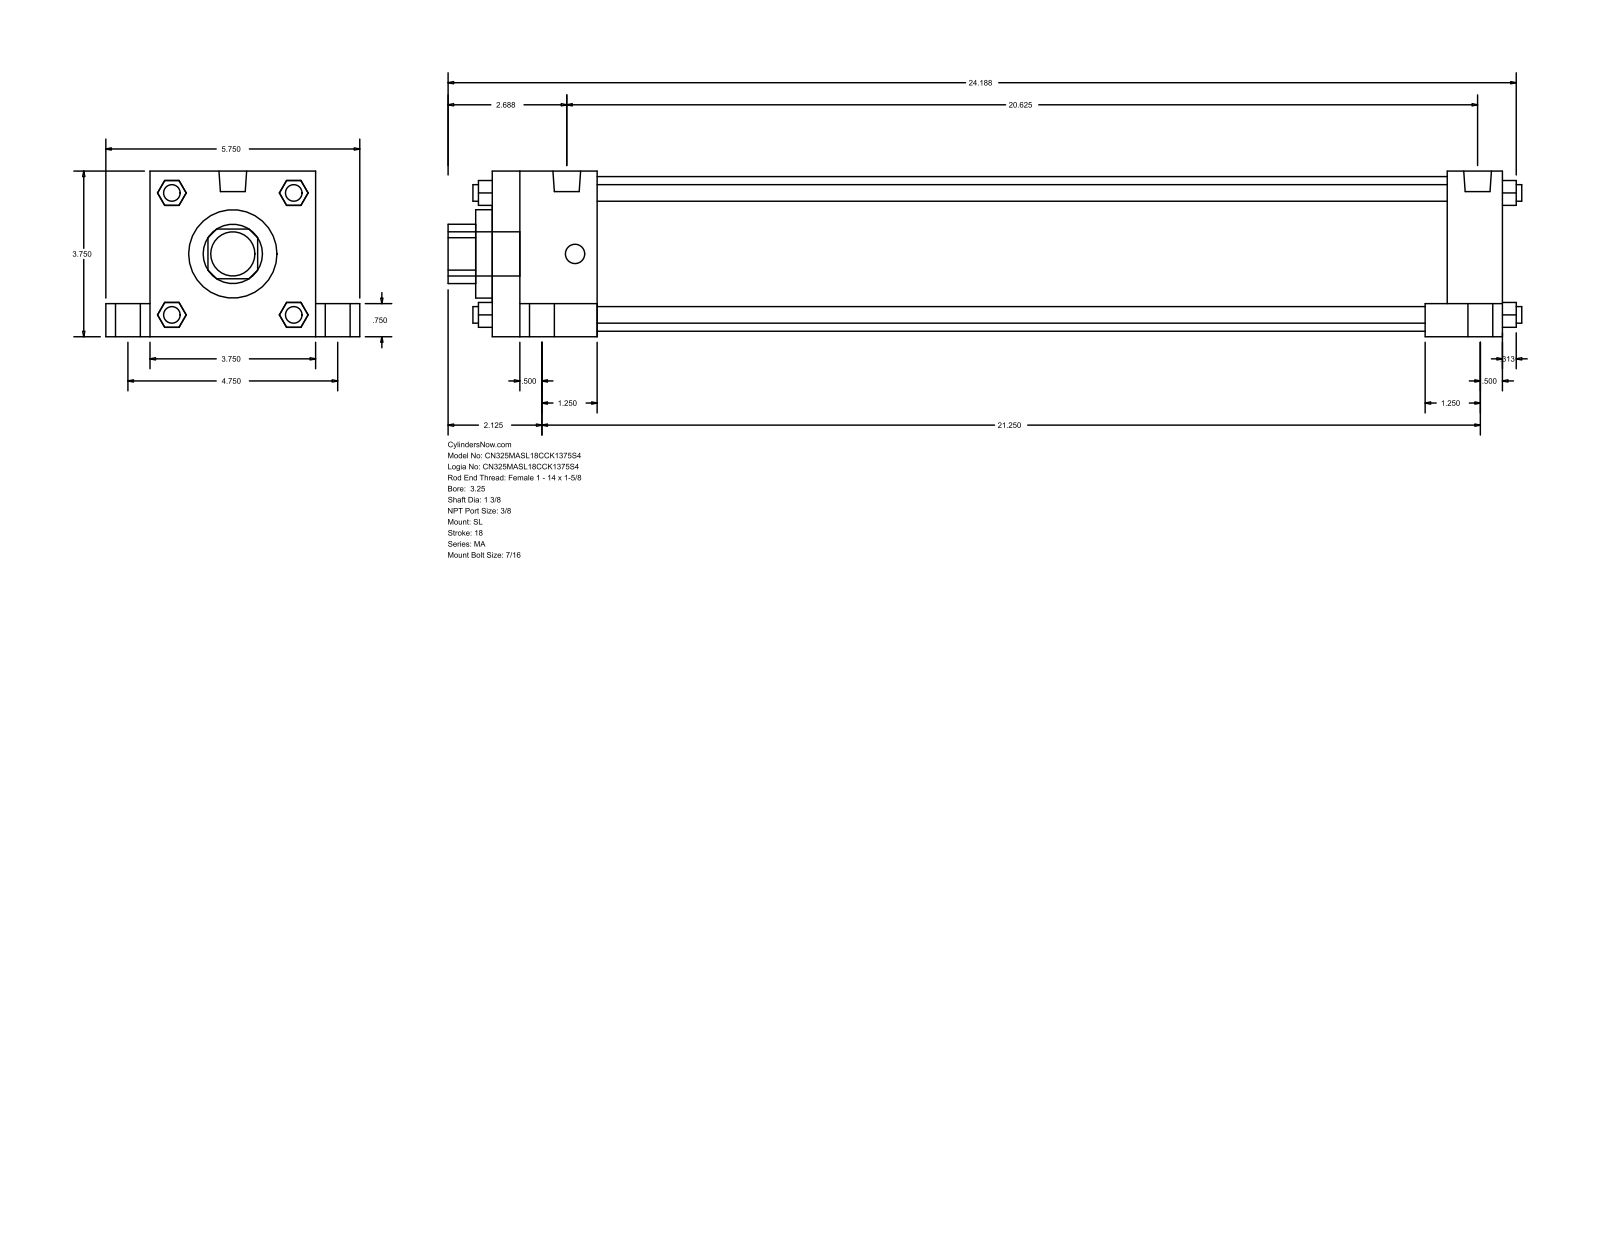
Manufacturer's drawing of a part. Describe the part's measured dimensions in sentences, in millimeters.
The part is named "MA_SL__0325_1.375". Its 3-D file was written by "GSSL Pune (CONFIG_CONTROL_DESIGN)". It is 0 solids with 148 faces: 112 planar, 36 cylindrical and 0 other. Overall it measures 617.54 by 146.05 by 95.25 millimeters. Round holes: 1 of diameter 34.92, 1 of diameter 50.8, 1 of diameter 88.9. Round bosses or shafts: 4 of diameter 20.64, 4 of diameter 14.29, 4 of diameter 11.11, 4 of diameter 9.53, 2 of diameter 15.93, 1 of diameter 25.4. Partial cylindrical surfaces (rounded edges, fillets, slot ends): 1 of radius 17.06. The main face-to-face distances are 95.24, 581.02, 488.95, 25.41, 120.65, 549.27, 31.75, 60.32, 520.7, 19.05.
